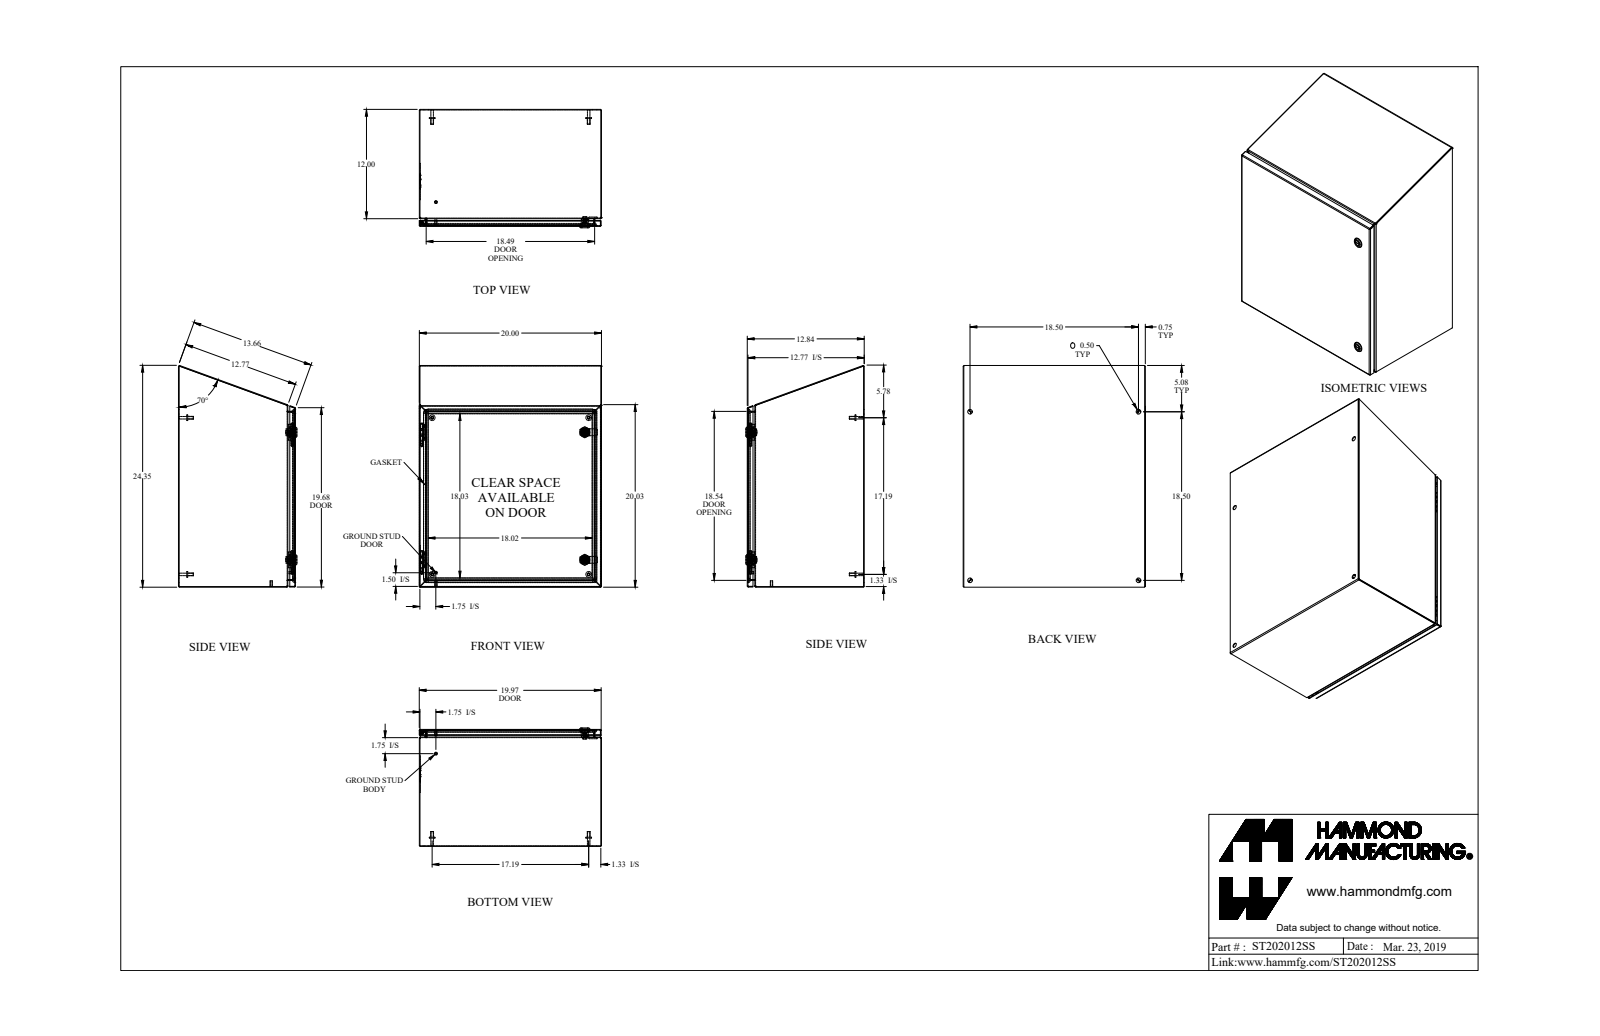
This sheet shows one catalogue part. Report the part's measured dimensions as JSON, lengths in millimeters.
{"part_name": "ST202012SS", "step_written_by": "SolidWorks 2018 (AUTOMOTIVE_DESIGN)", "units": "millimeters", "bodies": {"solids": 29, "faces": 746, "planar": 378, "cylindrical": 232, "other": 136}, "overall_size": [617.9, 508.2, 330.1], "volume_mm3": 2560000, "surface_area_mm2": 2783000, "round_holes": [[12.7, 6], [5, 2], [9.8, 2], [16, 2], [19.5, 2], [4.4, 1], [6.1, 1], [6.1, 1]], "round_bosses_or_shafts": [[8, 6], [15.9, 4], [7, 4], [27.9, 2], [19.9, 2], [15.9, 2], [13.3, 2], [6.4, 2]], "partial_cylinders_radius": [[0.9, 18], [2.7, 18], [4.8, 6], [0.2, 4], [1.6, 4], [3.2, 4], [6.4, 4], [12.7, 4]], "face_to_face_distances": [1.8, 324.2, 506.2, 322.4, 326.1, 504.3, 508, 303, 21.3, 23.1], "hole_center_spacings": [469.9, 664.5, 63.4, 63.5, 355.6, 413.6, 413.7, 446]}
